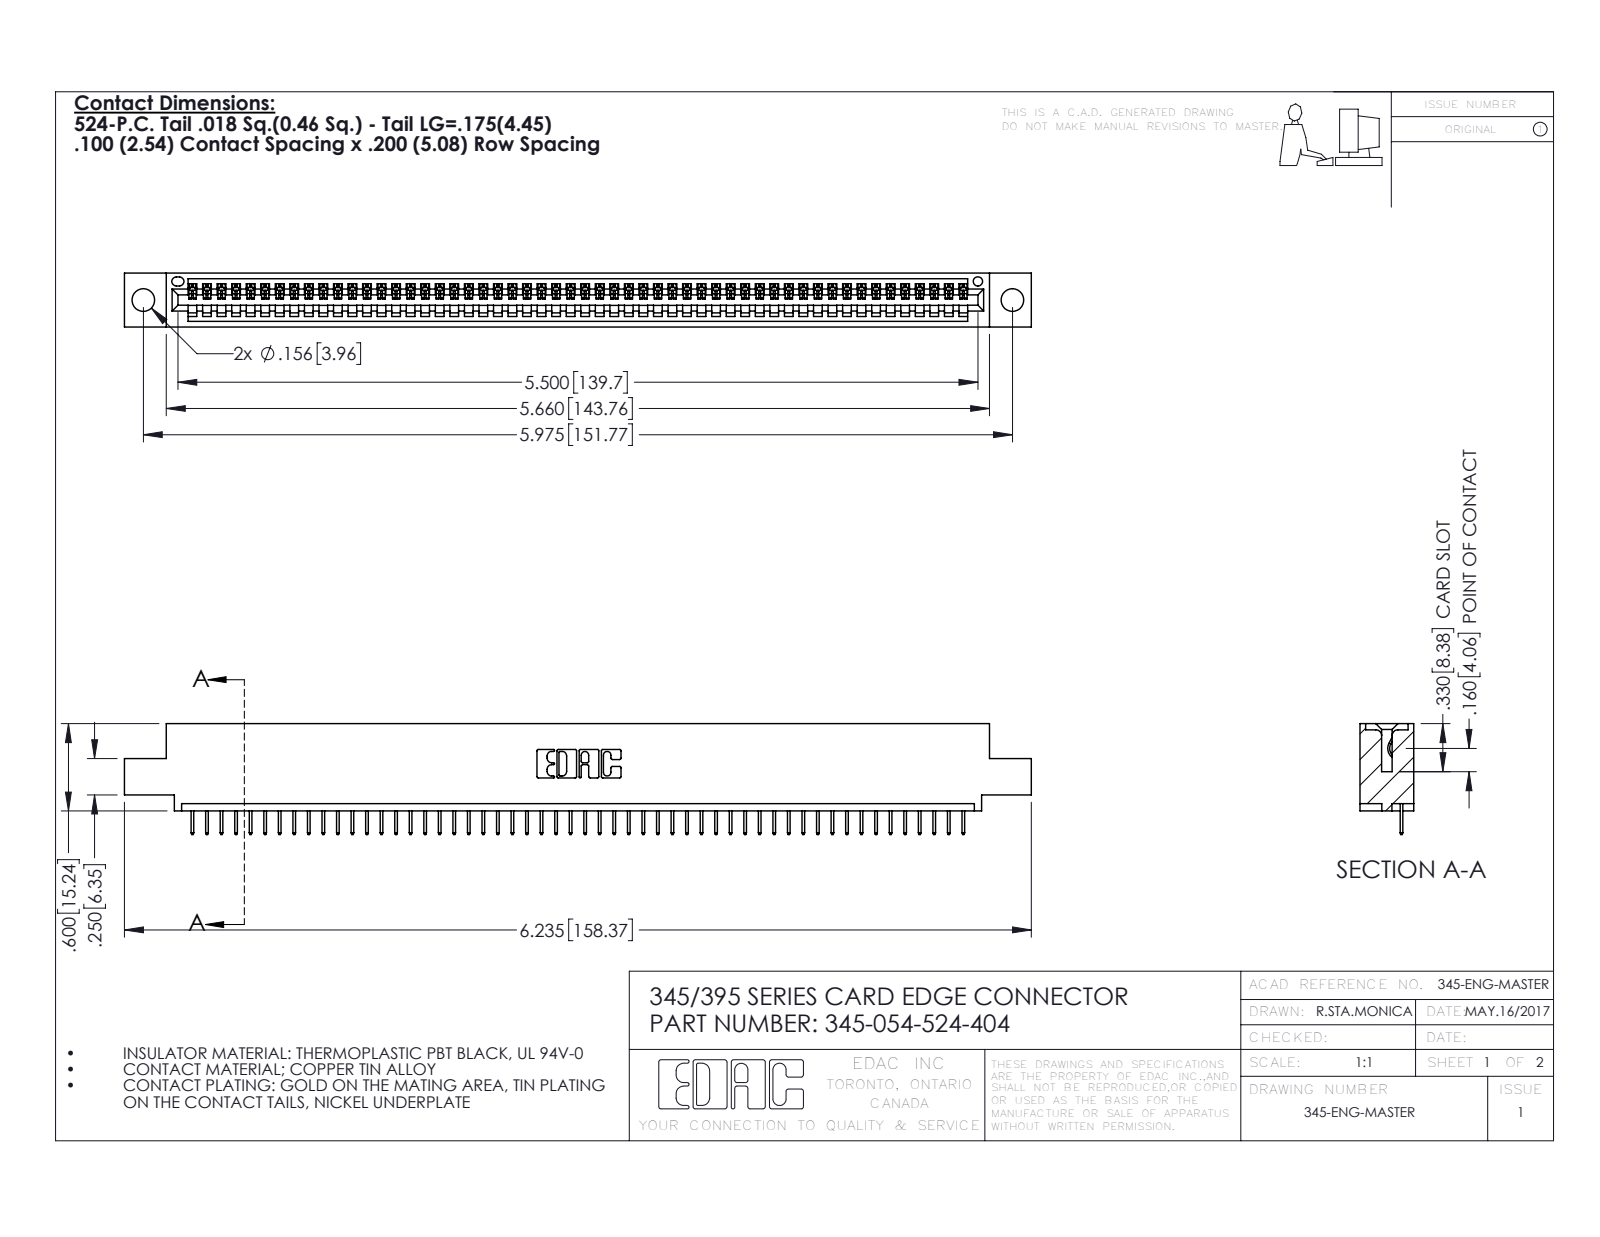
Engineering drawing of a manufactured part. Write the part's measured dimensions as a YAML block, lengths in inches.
part_name: "345 Part_0.110 Offset - 0.156 Dia-TH; 345-292-001_345-293-124; 345-054-524-404"
step_written_by: "SolidWorks 2016 (CONFIG_CONTROL_DESIGN)"
units: inches
bodies: {solids: 55, faces: 3478, planar: 2568, cylindrical: 910, other: 0}
overall_size: [6.235, 0.762, 0.37]
volume: 0.901
surface_area: 29.44
round_holes:
  - {diameter: 0.156, count: 2}
  - {diameter: 0.064, count: 1}
partial_cylinders:
  - {radius: 0.006, count: 108}
  - {radius: 0.01, count: 22}
  - {radius: 0.007, count: 6}
  - {radius: 0.031, count: 6}
  - {radius: 0.026, count: 3}
  - {radius: 0.031, count: 2}
  - {radius: 0.04, count: 2}
  - {radius: 0.014, count: 1}
face_to_face_distances: [0.072, 0.298, 0.37, 0.2, 0.098, 0.272, 0.025, 0.225, 0.072, 0.149]
hole_center_spacings: [0.27, 5.739, 5.975]
